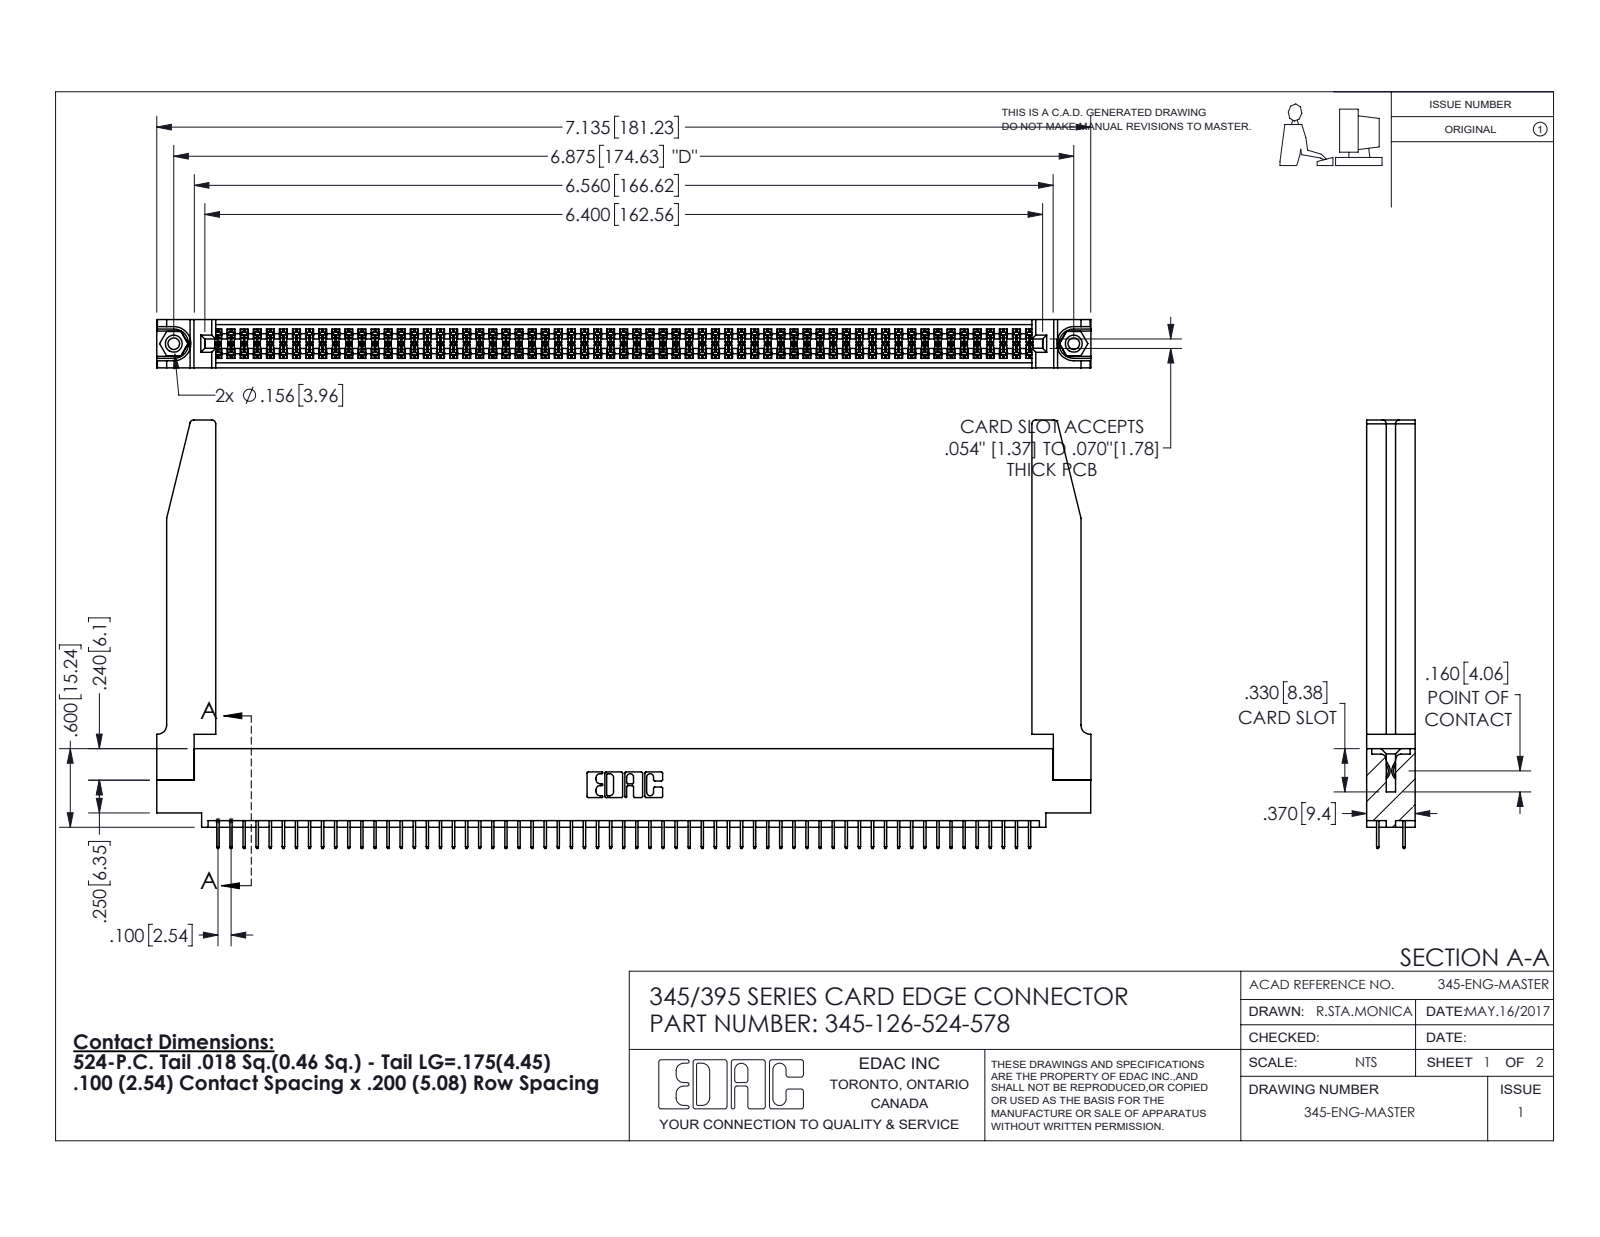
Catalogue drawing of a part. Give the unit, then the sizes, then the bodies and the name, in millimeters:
Units: millimetres
Overall size (bounding box): 181.3 × 83.1 × 9.4
Round holes (diameter × count): ⌀2.3 ×2, ⌀3.2 ×2, ⌀4 ×2, ⌀1.6 ×1
Round bosses / shafts (diameter × count): ⌀3.9 ×2
Partial cylindrical surfaces — rounded edges, fillets, slot ends (radius × count): R0.2 ×189, R0.3 ×22, R0.8 ×8, R0.2 ×6, R0.8 ×6, R0.7 ×3, R0.4 ×2, R0.5 ×2
Main face-to-face distances: 1.8, 9.4, 7.6, 5.1, 2.5, 6.9, 0.6, 5.7, 1.8, 4.4
Hole centre spacings: 6.9, 168.6, 174.6
Volume: 25 300 mm³ · Surface area: 32 760 mm²
Bodies: 131 solids, 7168 faces (5140 planar, 1976 cylindrical, 52 other)
Part name (STEP PRODUCT): 345-292-001_345-293-124; 345-126-524-578; 345-250-001_345-250-001-102; 345 Part_0.110 Offset - 0.156 Dia-TH (+1 more)
STEP written by: SolidWorks 2016 (CONFIG_CONTROL_DESIGN)
